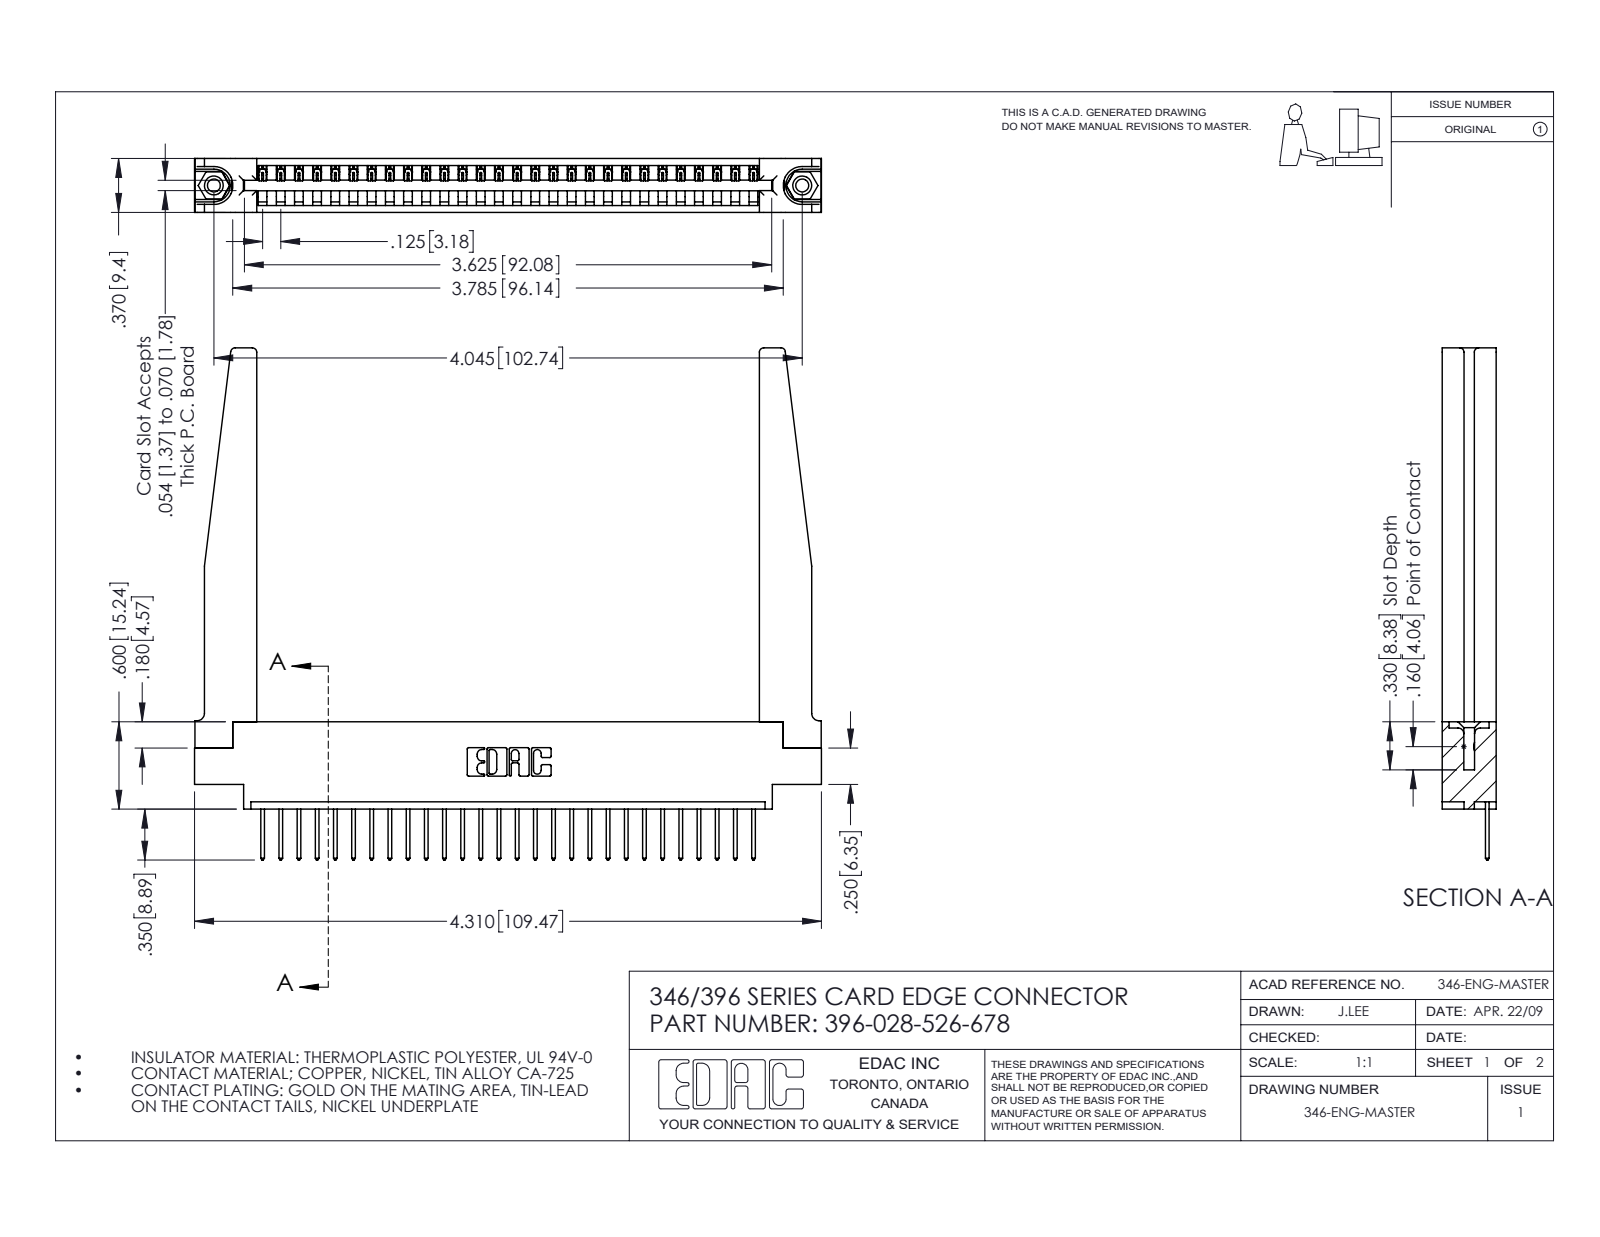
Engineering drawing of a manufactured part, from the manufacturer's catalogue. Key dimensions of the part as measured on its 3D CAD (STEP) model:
Part name (STEP PRODUCT): 346 Part_0.170 Offset - 0.156 Dia-TH; 396-028-526-678; 345-250-001_345-250-001-102; 346-220-078_345-220-078 (+1 more)
STEP written by: SolidWorks 2016 (CONFIG_CONTROL_DESIGN)
Units: inches
Bodies: 33 solids, 1984 faces (1342 planar, 590 cylindrical, 52 other)
Overall size (bounding box): 4.31 × 3.52 × 0.37
Volume: 1.044 in³ · Surface area: 29.88 in²
Round holes (diameter × count): ⌀0.089 ×2, ⌀0.125 ×2, ⌀0.156 ×2, ⌀0.064 ×1
Round bosses / shafts (diameter × count): ⌀0.155 ×2
Partial cylindrical surfaces — rounded edges, fillets, slot ends (radius × count): R0.006 ×56, R0.01 ×56, R0.01 ×22, R0.03 ×8, R0.007 ×6, R0.031 ×6, R0.026 ×3, R0.031 ×2
Main face-to-face distances: 0.37, 0.048, 0.322, 0.072, 0.148, 0.15, 0.25, 0.298, 0.025, 0.222
Hole centre spacings: 0.246, 3.837, 4.045
